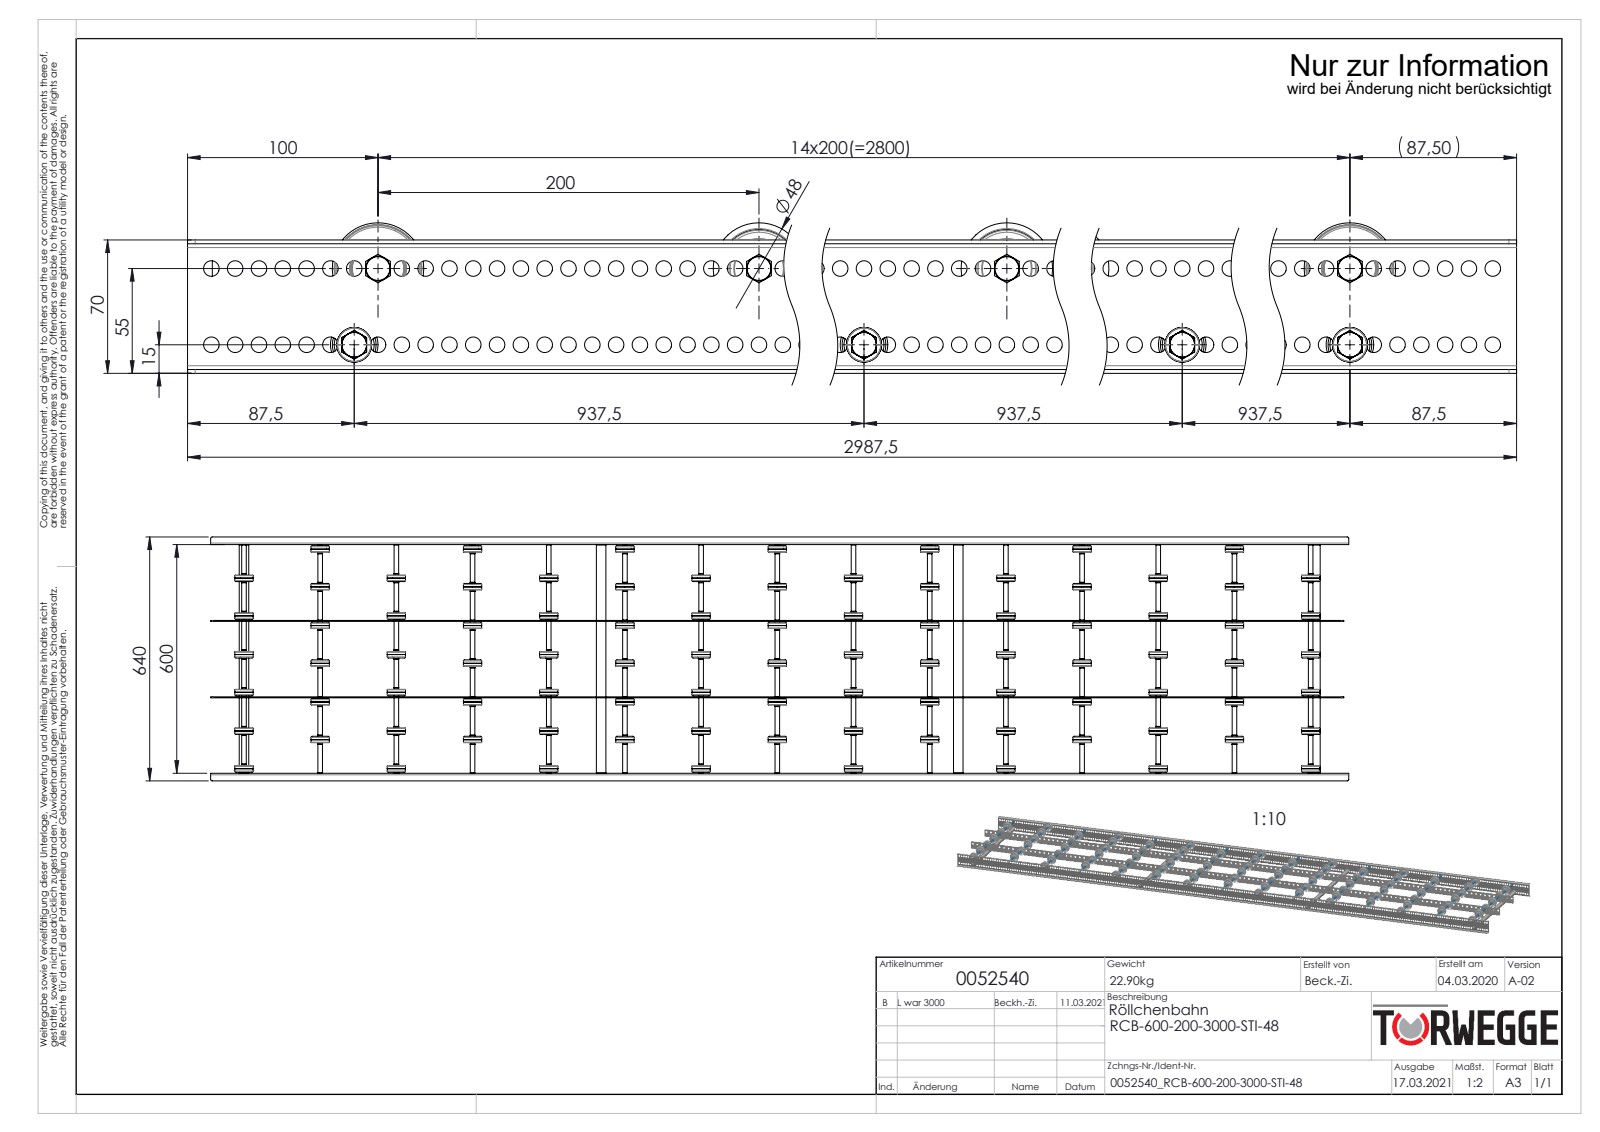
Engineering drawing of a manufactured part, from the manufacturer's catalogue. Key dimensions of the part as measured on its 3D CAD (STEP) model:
Part name (STEP PRODUCT): 0046278_KB-ROHR-12X1,75mm_KFG_L75; Hutmutter_DIN_1587_M8; S100100_Längstraverse-42x2,5_S100104_Lngstraverse-RB-L3000; Traversen_KFG_L600 (+6 more)
STEP written by: SolidWorks 2020 (AUTOMOTIVE_DESIGN)
Units: millimetres
Bodies: 339 solids, 11608 faces (2106 planar, 5334 cylindrical, 4168 other)
Overall size (bounding box): 2987.5 × 640 × 79
Volume: 4 780 000 mm³ · Surface area: 3 929 000 mm²
Round holes (diameter × count): ⌀8.2 ×476, ⌀8.5 ×119, ⌀6.65 ×15, ⌀8 ×15, ⌀9.65 ×15, ⌀15 ×15, ⌀41 ×15, ⌀6.8 ×4, ⌀21 ×4
Round bosses / shafts (diameter × count): ⌀48 ×15, ⌀13 ×15, ⌀12.5 ×15, ⌀12.4 ×15, ⌀12 ×15, ⌀11.5 ×15, ⌀25 ×4, ⌀8 ×4
Partial cylindrical surfaces — rounded edges, fillets, slot ends (radius × count): R4 ×8, R2 ×4, R5 ×4
Main face-to-face distances: 200.5, 2, 602, 2.5, 198, 401, 68, 604, 600, 99
Hole centre spacings: 12.5, 25, 37.5, 50, 62.5, 75, 87.5, 100
